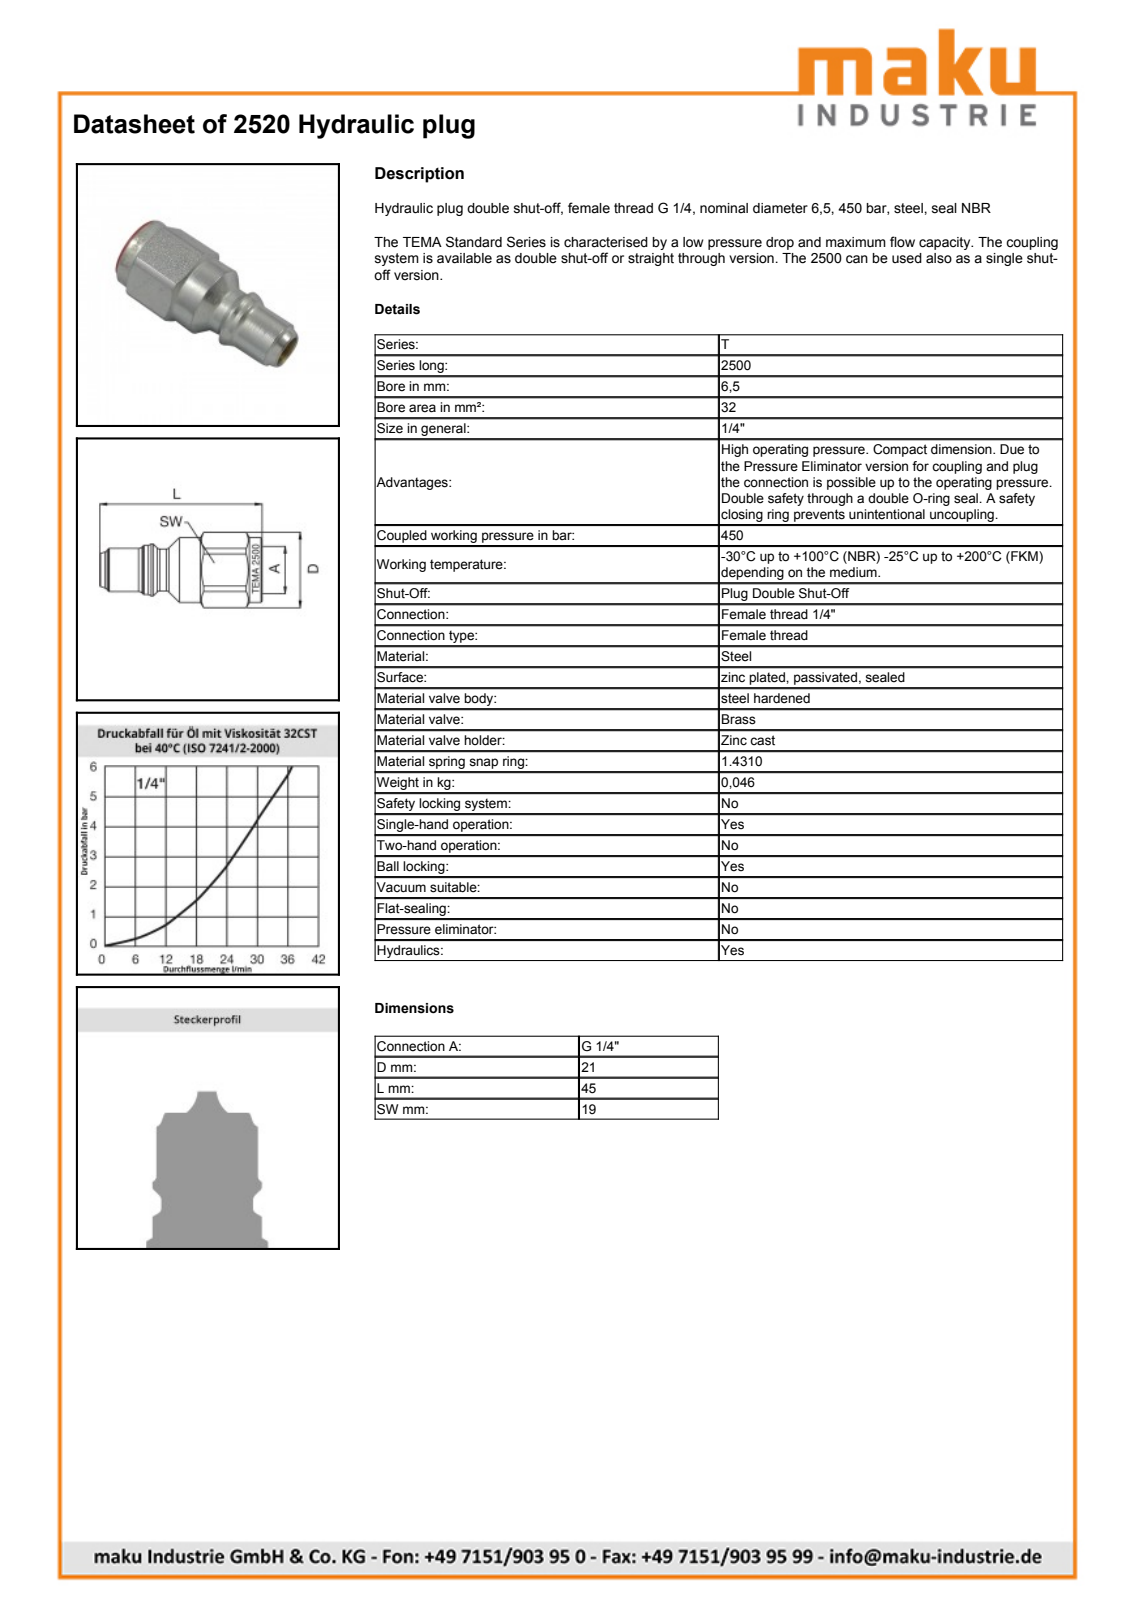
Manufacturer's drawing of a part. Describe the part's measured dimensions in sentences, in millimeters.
The part is named "2520". Its 3-D file was written by "SolidWorks 2009 (AUTOMOTIVE_DESIGN)". It is 1 solid with 65 faces: 11 planar, 24 cylindrical and 30 other. Overall it measures 44.5 by 21 by 19 millimeters. Its volume is 7 509 cubic millimeters and its surface area 3 553 square millimeters. Round holes: 1 of diameter 6.4, 1 of diameter 7.45, 1 of diameter 11.7. Round bosses or shafts: 1 of diameter 18.55, 1 of diameter 14.65, 1 of diameter 13.6, 1 of diameter 12.2. Partial cylindrical surfaces (rounded edges, fillets, slot ends): 1 of radius 10.5. The main face-to-face distances are 19, 13.5, 16, 29.5, 15, 31, 44.5, 14.7, 30.7, 44.2.
